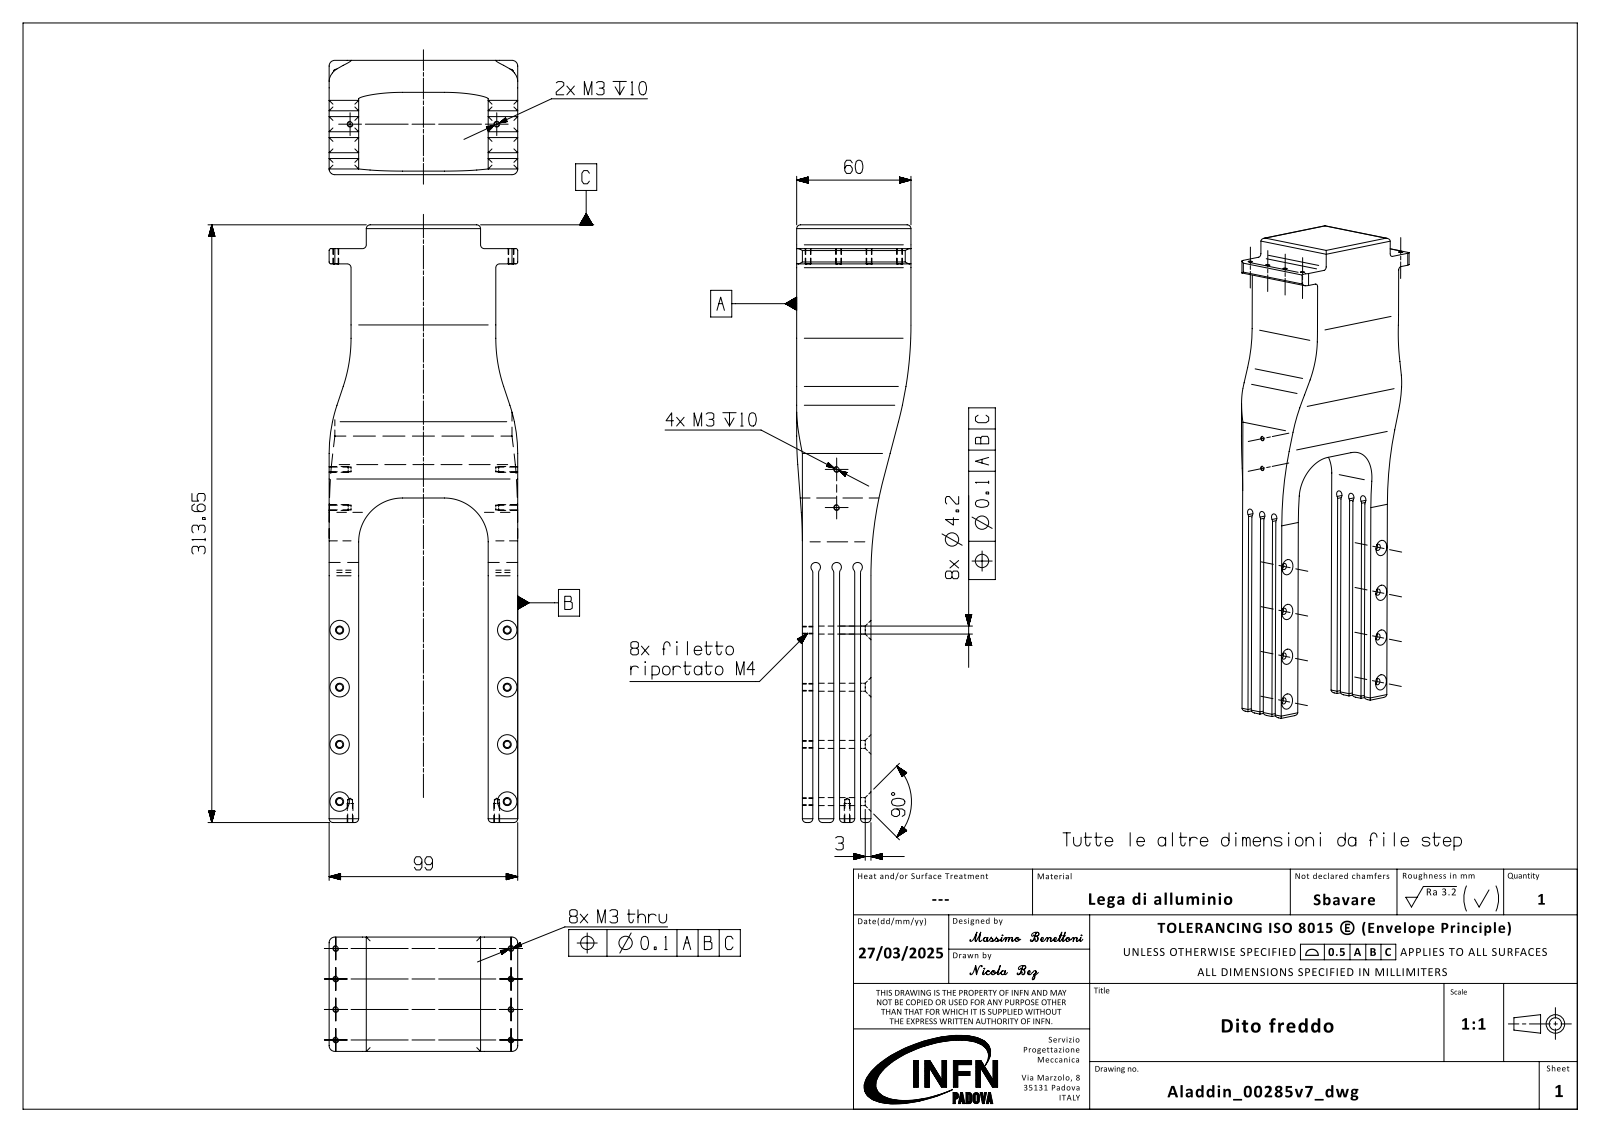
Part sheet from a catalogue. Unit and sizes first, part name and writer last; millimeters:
Units: millimetres
Overall size (bounding box): 313.65 × 99 × 60
Round holes (diameter × count): ⌀2.5 ×12, ⌀3.3 ×8, ⌀4.2 ×8
Partial cylindrical surfaces — rounded edges, fillets, slot ends (radius × count): R2 ×26, R1 ×4, R3 ×4, R80 ×4, R200 ×4, R2.5 ×3, R23 ×2
Main face-to-face distances: 11, 3.05, 15.5, 83.5, 14.05, 22, 7.95, 99, 4, 68
Hole centre spacings: 16, 30, 92.97, 93.38, 32, 60, 88, 92
Volume: 825 442 mm³ · Surface area: 108 981 mm²
Bodies: 1 solid, 193 faces (50 planar, 125 cylindrical, 18 other)
Part name (STEP PRODUCT): IR3_00000285_v7_objects
STEP written by: SIEMENS PLM Software NX2306.9102 (AUTOMOTIVE_DESIGN)
